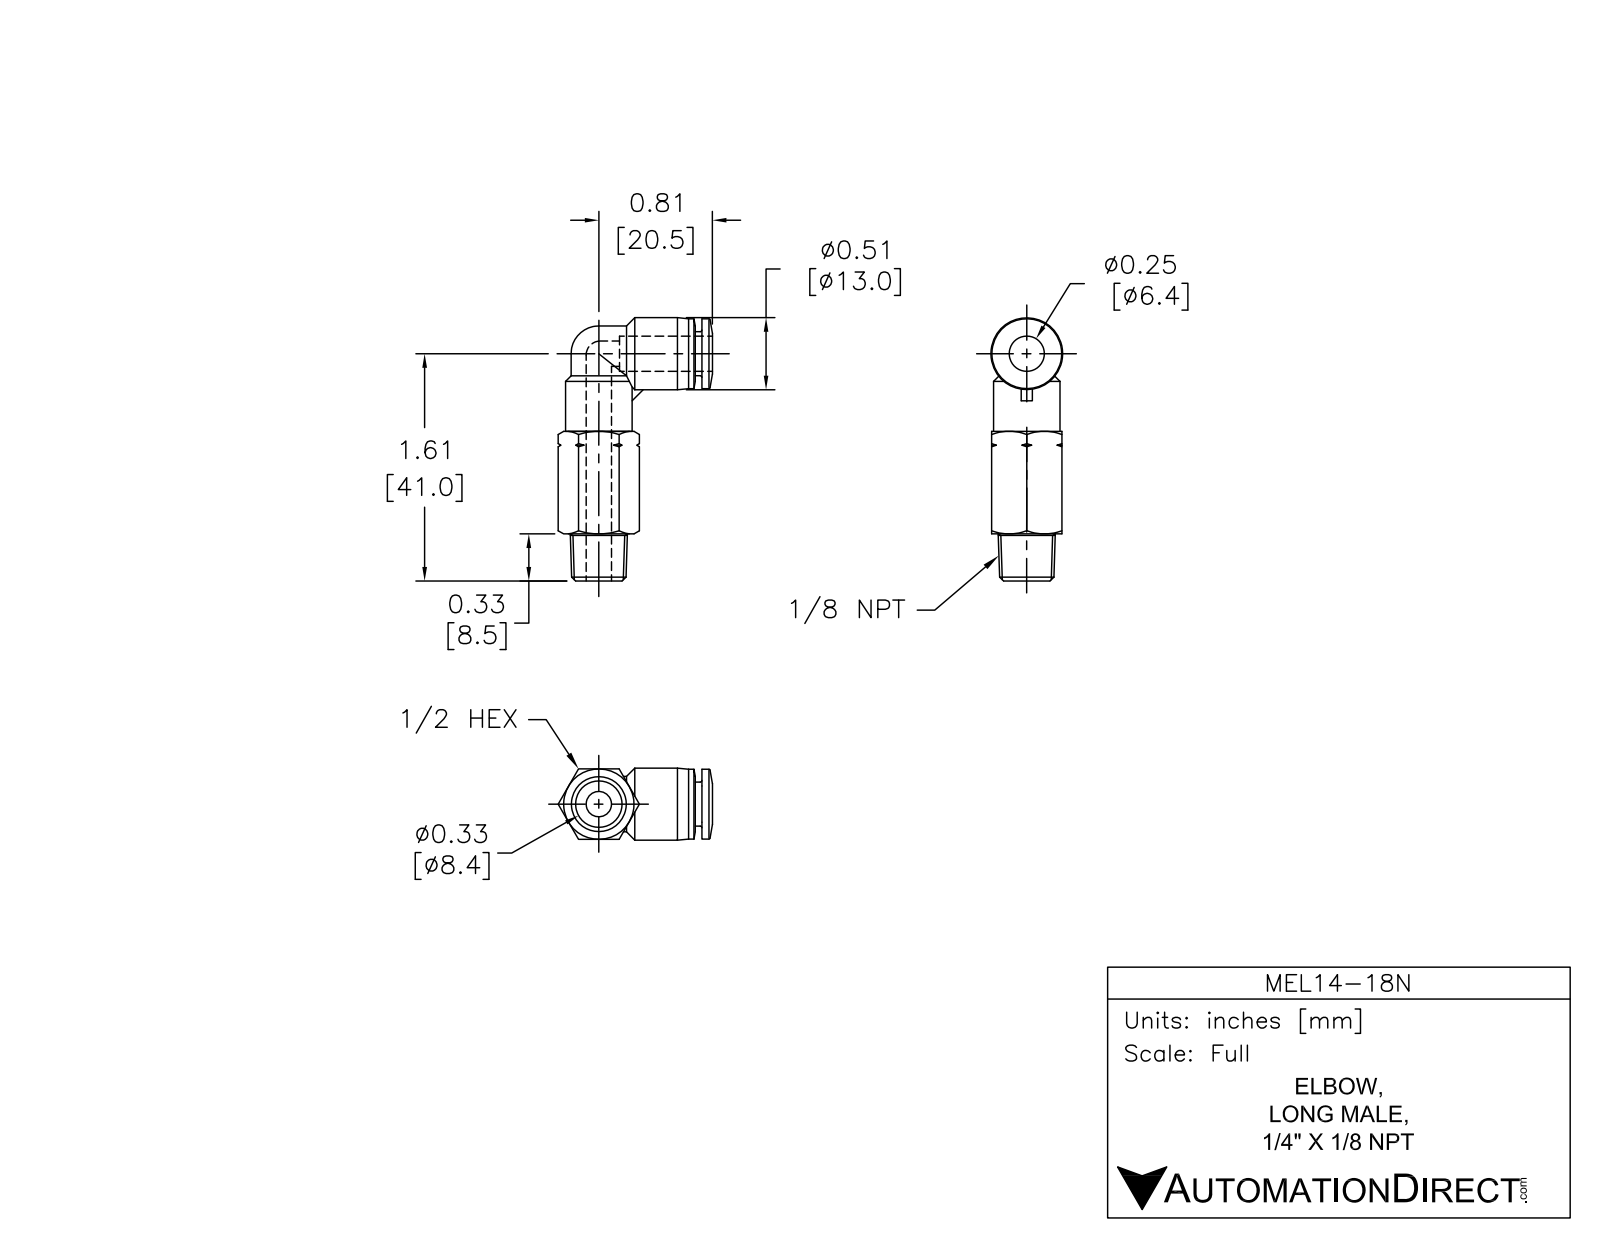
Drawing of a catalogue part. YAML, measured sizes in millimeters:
part_name: "MEL14-18N"
step_written_by: "SolidWorks 2015 (AUTOMOTIVE_DESIGN)"
units: millimeters
bodies: {solids: 1, faces: 88, planar: 15, cylindrical: 20, other: 53}
overall_size: [47.5, 27.8, 13]
volume: 5600
surface_area: 3660
round_holes:
  - {diameter: 4.5, count: 2}
  - {diameter: 6.6, count: 1}
round_bosses_or_shafts:
  - {diameter: 10, count: 2}
  - {diameter: 13, count: 1}
  - {diameter: 12.6, count: 1}
  - {diameter: 12, count: 1}
  - {diameter: 8, count: 1}
face_to_face_distances: [12.7, 8.5, 1.2, 13.7, 14.9, 27, 18.5, 5.4, 7.3, 2]
